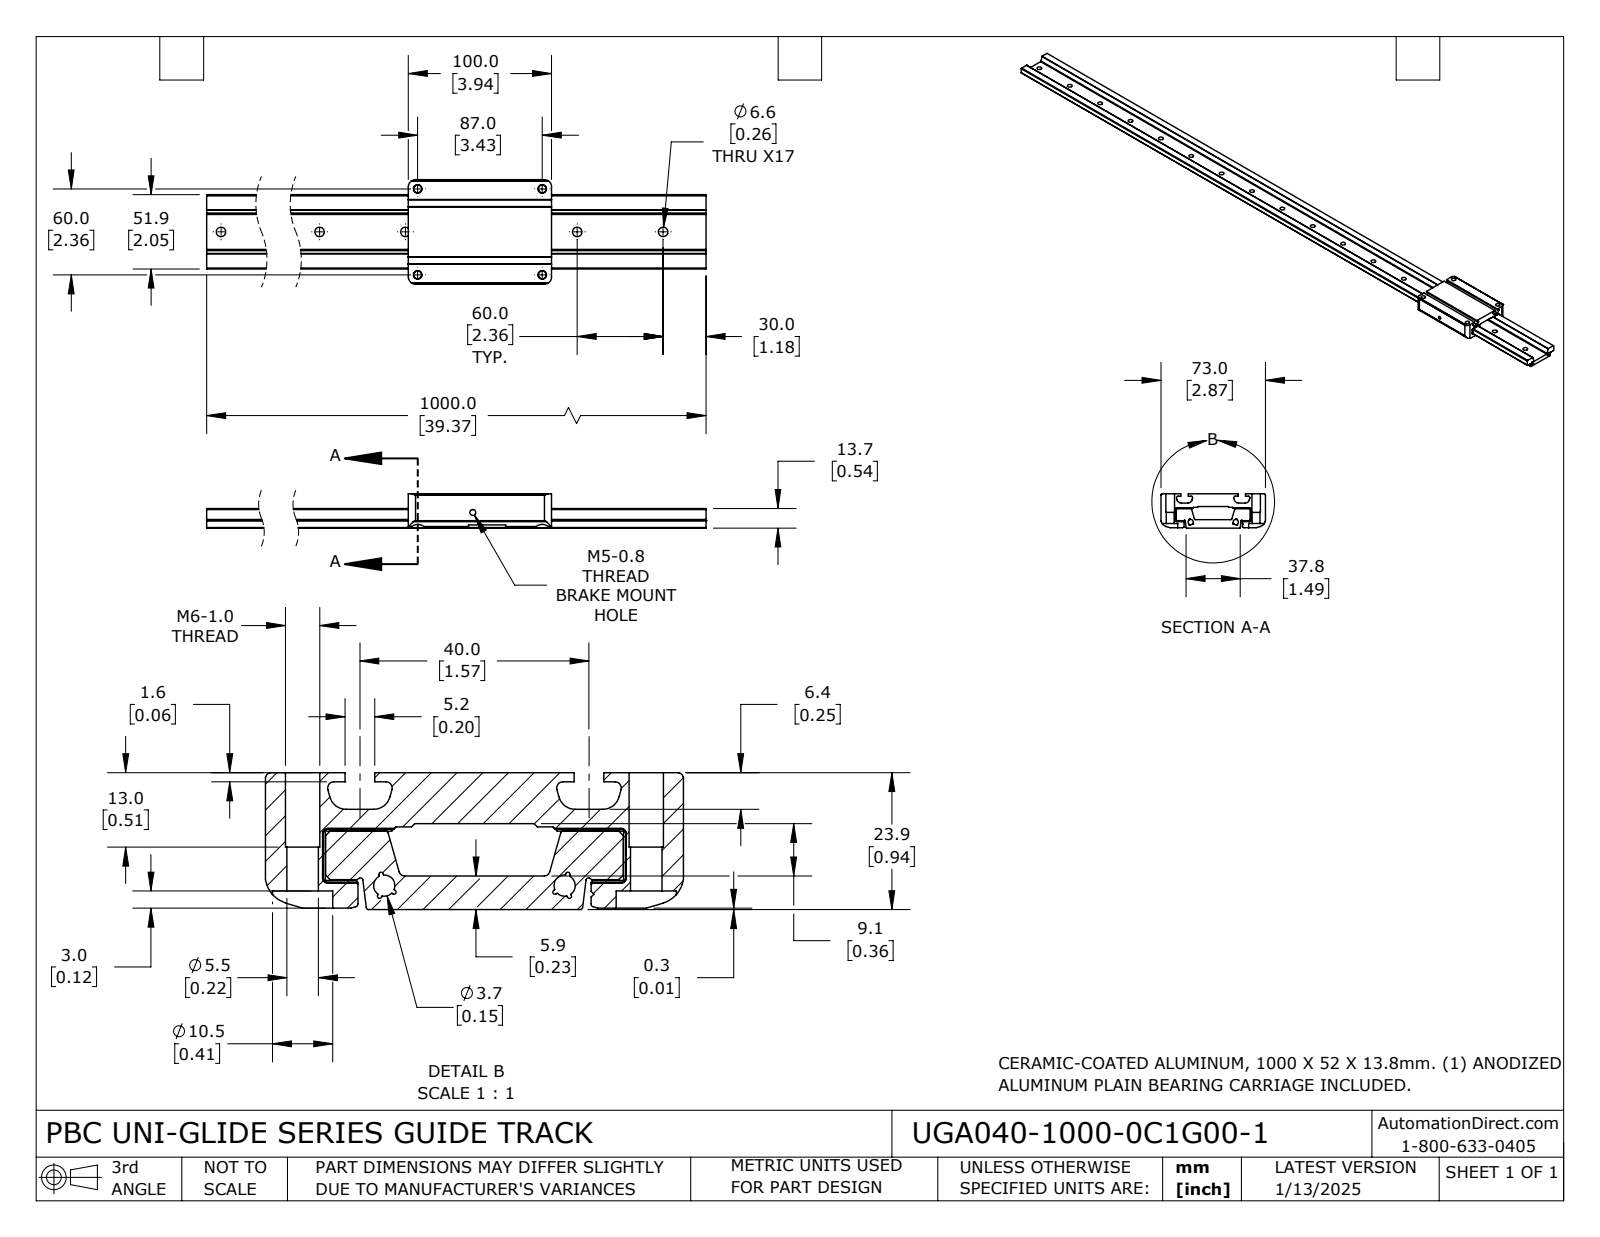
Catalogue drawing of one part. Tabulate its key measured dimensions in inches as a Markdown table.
| quantity | value |
| --- | --- |
| part name | UGA040-1000-0C1G00-1_RAIL; UGA040-1000-0C1G00-1_CARRIAGE; UGA040-1000-0C1G00-1 |
| STEP written by | SolidWorks 2023 (CONFIG_CONTROL_DESIGN) |
| units | inches |
| bodies | 10 solids, 416 faces (214 planar, 183 cylindrical, 19 other) |
| overall size | 39.37 × 2.874 × 0.941 |
| volume | 29 in³ |
| surface area | 333.8 in² |
| round holes (diameter × count) | 0.261 × 17, 0.098 × 4, 0.118 × 4, 0.217 × 4, 0.236 × 4, 0.413 × 4, 0.146 × 2, 0.165 × 1 |
| partial cylindrical surfaces (radius × count) | 0.039 × 8, 0.094 × 8, 0.015 × 6, 0.02 × 6, 0.197 × 6, 0.035 × 4, 0.043 × 4, 0.118 × 4 |
| main face-to-face distances | 0.231, 0.539, 0.308, 0.333, 0.207, 0.024, 2.045, 0.941, 0.734, 0.71 |
| hole center spacings | 2.362, 4.724, 7.087, 9.449, 11.811, 14.173, 16.535, 18.898 |
